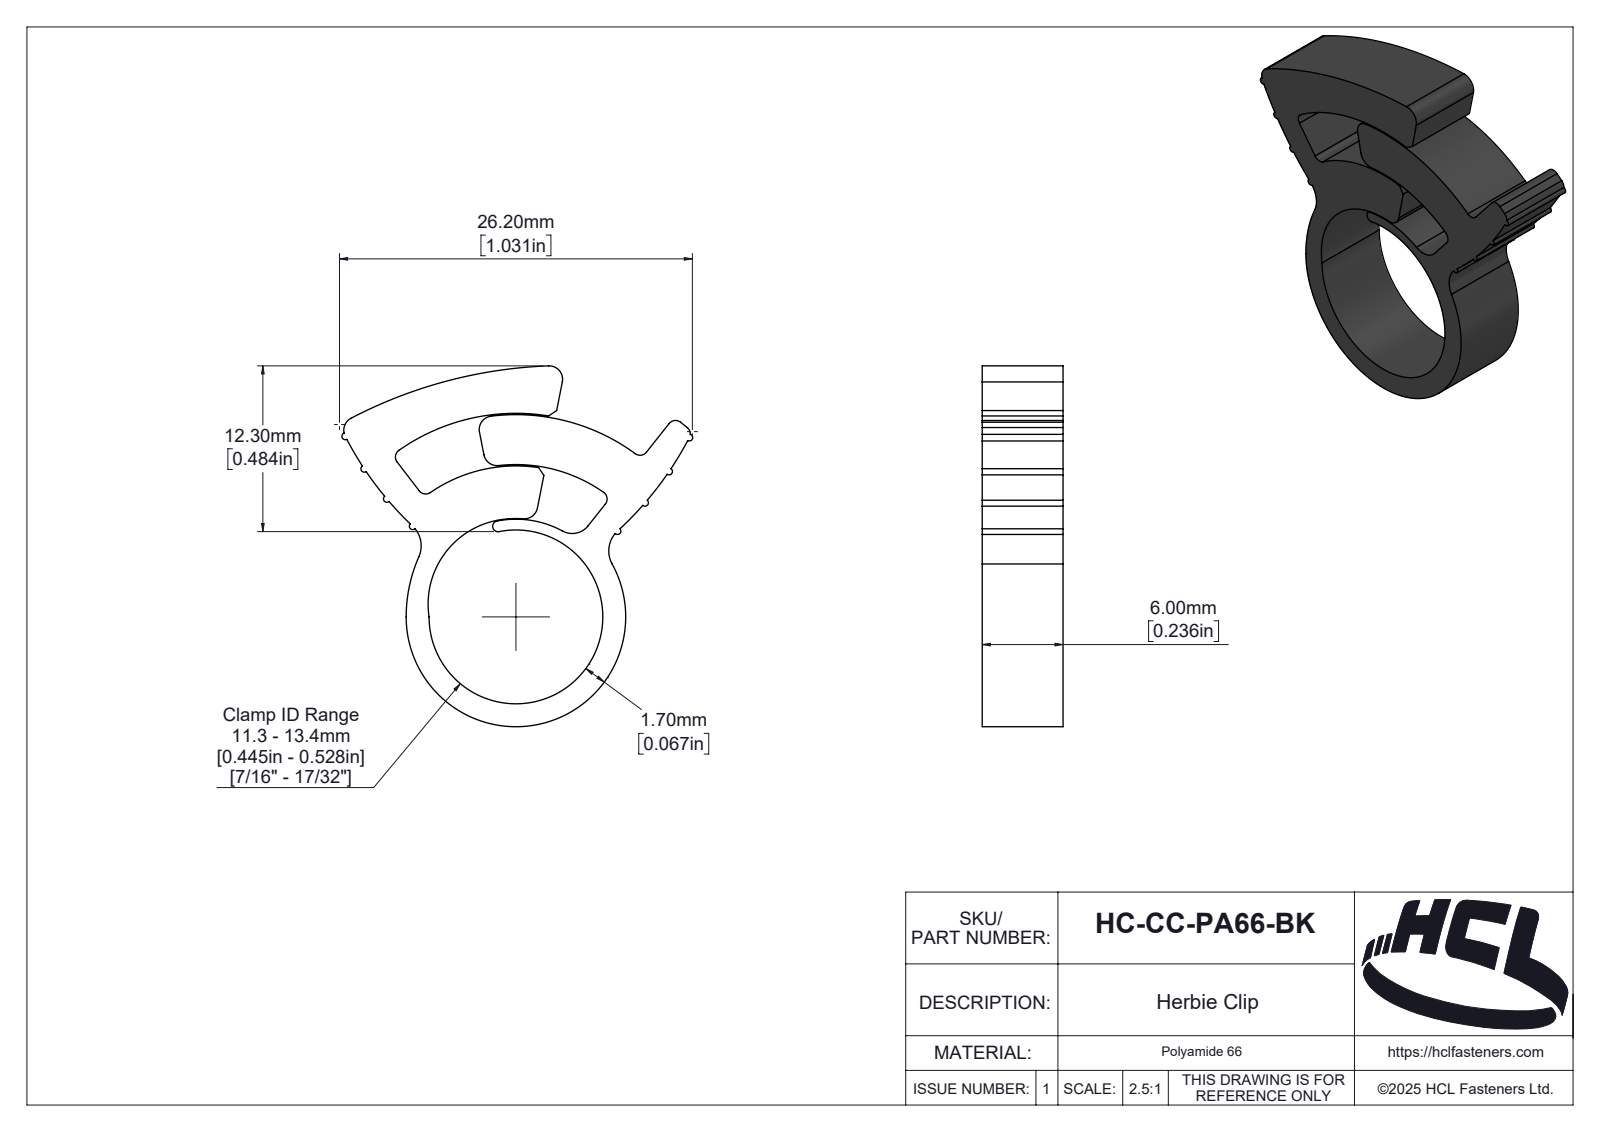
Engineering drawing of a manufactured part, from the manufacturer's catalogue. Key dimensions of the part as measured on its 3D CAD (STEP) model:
Part name (STEP PRODUCT): HC-CC-PA66-BK
STEP written by: SolidWorks 2025 (AUTOMOTIVE_DESIGN)
Units: millimetres
Bodies: 1 solid, 162 faces (13 planar, 100 cylindrical, 49 other)
Overall size (bounding box): 26.78 × 26.05 × 6
Volume: 1 397 mm³ · Surface area: 1 639 mm²
Partial cylindrical surfaces — rounded edges, fillets, slot ends (radius × count): R0.25 ×8, R0.6 ×6, R1 ×5, R2 ×2, R0.17 ×1, R0.4 ×1, R0.67 ×1, R0.84 ×1
Main face-to-face distances: 6
